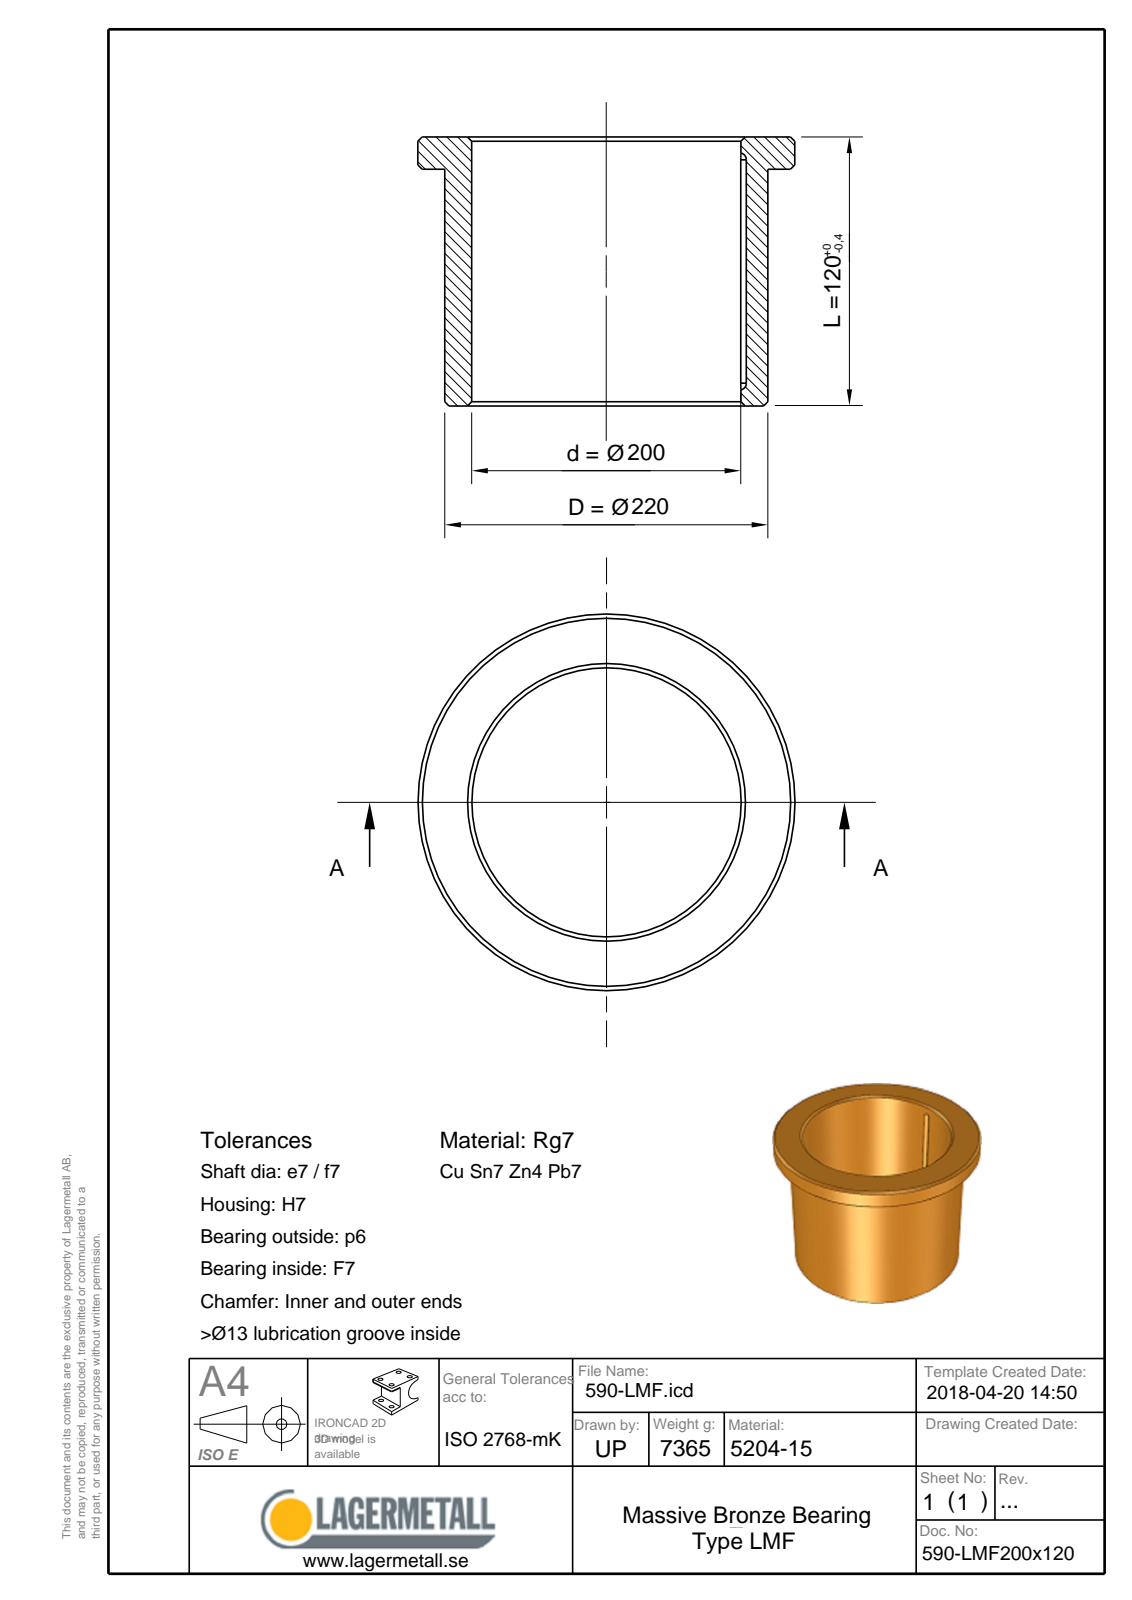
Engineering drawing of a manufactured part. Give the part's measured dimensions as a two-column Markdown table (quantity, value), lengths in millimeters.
| quantity | value |
| --- | --- |
| part name | 590-LMF200x120 |
| STEP written by | Spatial InterOp 3D (CONFIG_CONTROL_DESIGN) |
| units | millimeters |
| bodies | 1 solid, 16 faces (6 planar, 5 cylindrical, 5 other) |
| overall size | 235 × 235 × 120 |
| volume | 836 941 mm³ |
| surface area | 179 280 mm² |
| round holes (diameter × count) | 200 × 1 |
| round bosses / shafts (diameter × count) | 235 × 1, 220 × 1 |
| partial cylindrical surfaces (radius × count) | 2.75 × 2 |
| main face-to-face distances | 120, 110, 10, 5.5 |
